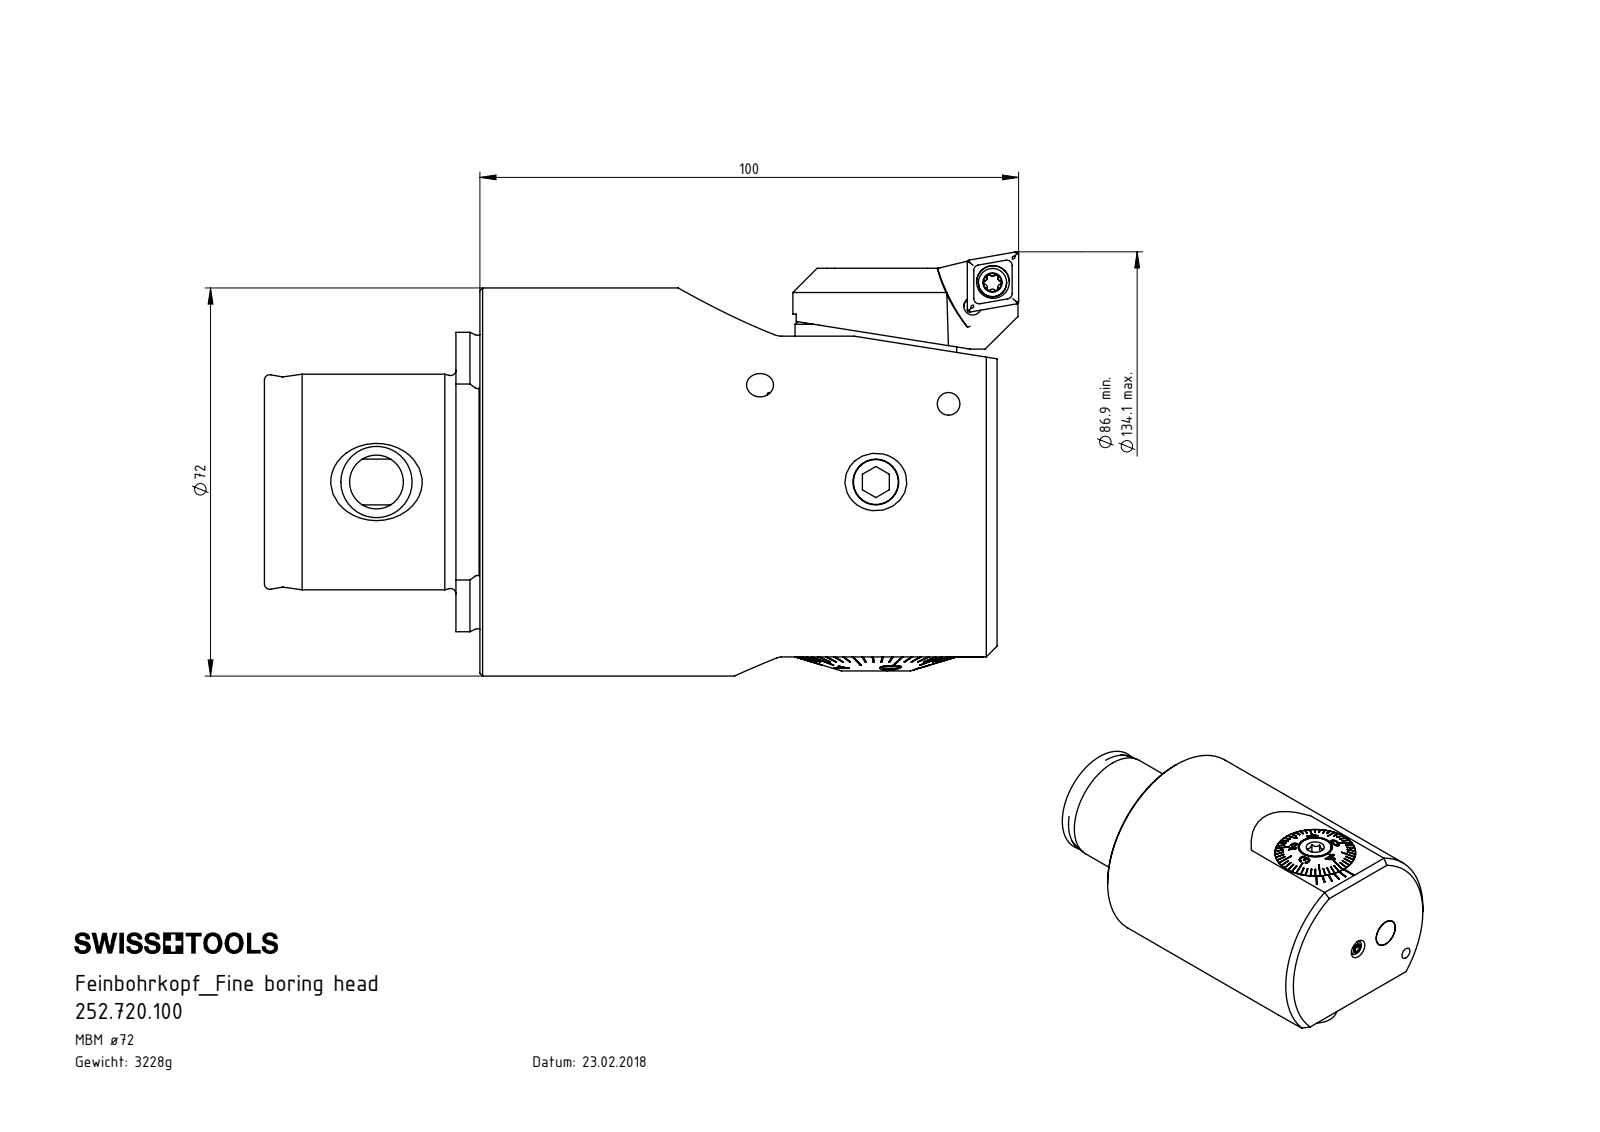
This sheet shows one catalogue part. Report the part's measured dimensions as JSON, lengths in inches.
{"part_name": "F72-BG1.DA3.030_A; ISO 4026 - M10 x 16; WCB-ER2.001.009_A; DIN 7984 - M10 x 16 (+8 more)", "step_written_by": "SolidWorks 2017 (AUTOMOTIVE_DESIGN)", "units": "inches", "bodies": {"solids": 13, "faces": 567, "planar": 306, "cylindrical": 81, "other": 180}, "overall_size": [5.354, 2.979, 2.835], "volume_in3": 25.25, "surface_area_in2": 97.79, "round_holes": [[0.098, 3], [0.165, 3], [0.335, 3], [0.13, 2], [0.394, 2], [0.197, 1], [0.315, 1], [0.449, 1], [0.472, 1], [0.488, 1], [0.512, 1], [0.551, 1]], "round_bosses_or_shafts": [[0.394, 2], [2.835, 1], [1.575, 1], [1.181, 1], [1.18, 1], [1.177, 1], [0.984, 1], [0.709, 1]], "partial_cylinders_radius": [[0.013, 6], [0.023, 6], [0.098, 6], [0.079, 4], [0.126, 3], [0.02, 2], [0.039, 1], [0.138, 1]], "face_to_face_distances": [3.78, 1.575, 5.354, 2.087, 1.4, 0.175, 3.955, 0.102, 0.256, 2.445], "hole_center_spacings": [0.571, 0.707, 0.78, 1.142, 3.65, 4.22]}
